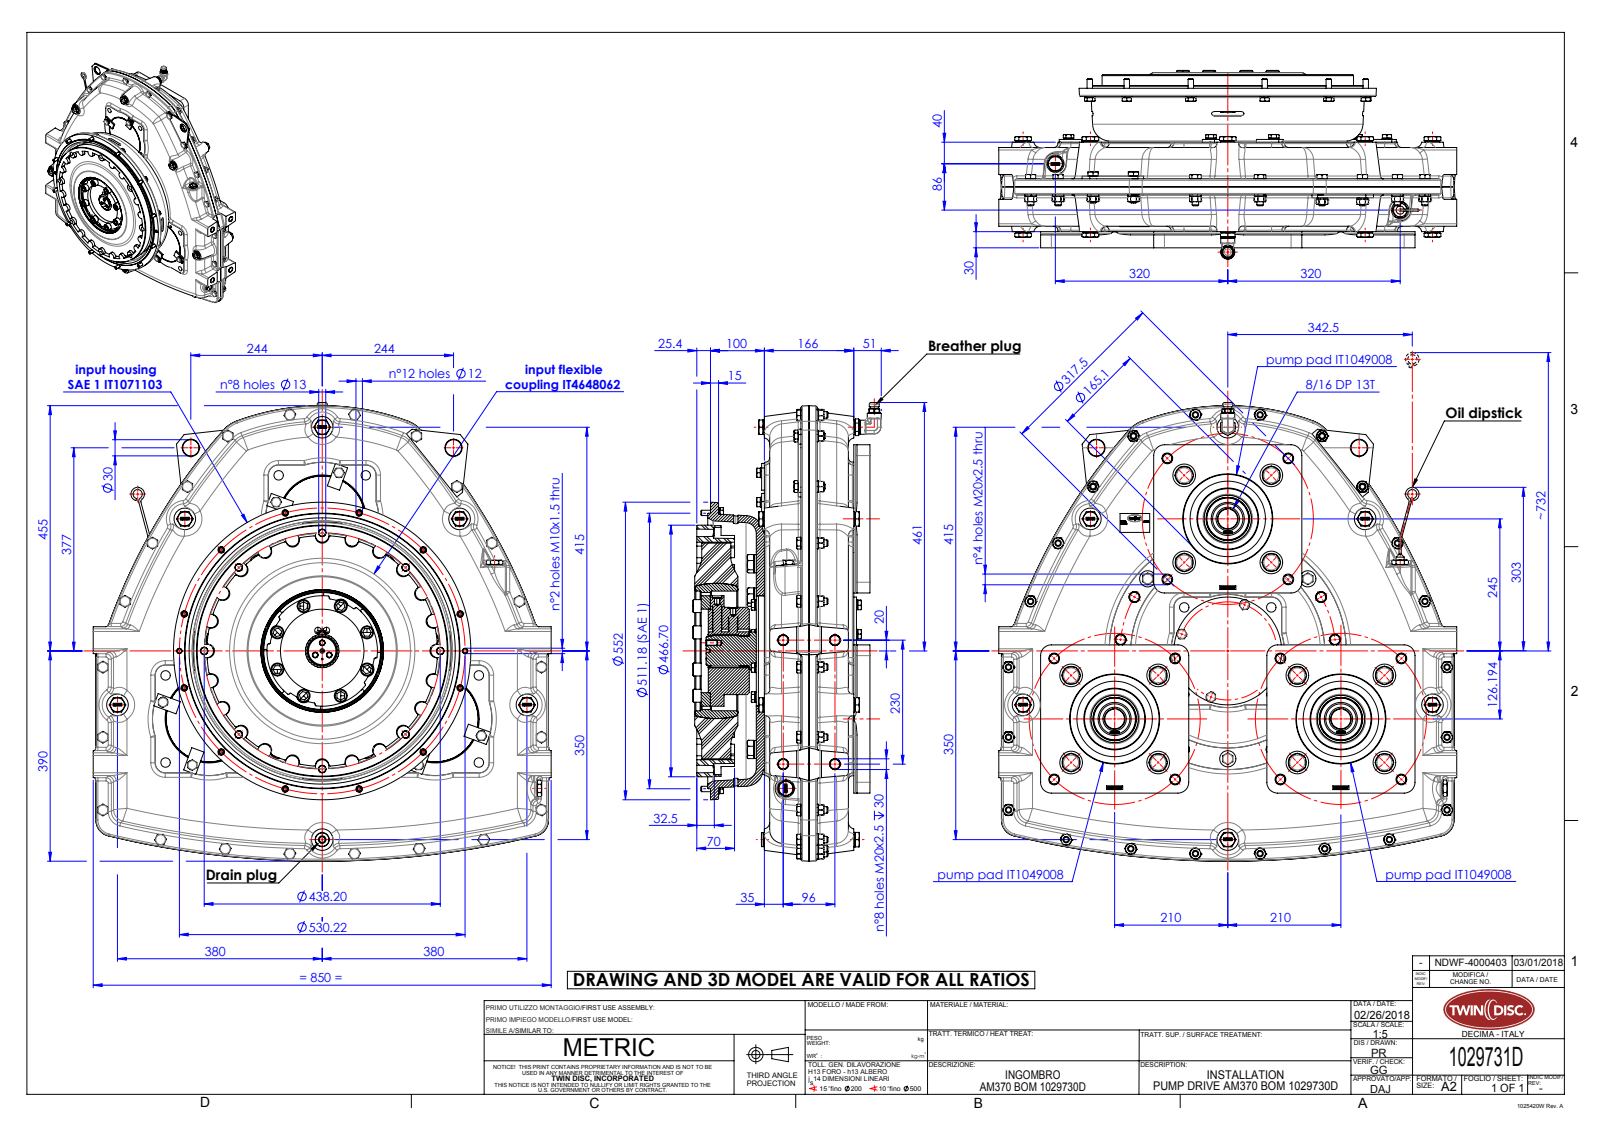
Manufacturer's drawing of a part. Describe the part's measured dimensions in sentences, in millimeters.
The part is named "ITam370-002_rev00-installation; IT2021490_rev00-installation; ITam270-014_rev00-installation; ITam365-006_rev00-installation (+8 more)". Its 3-D file was written by "SolidWorks 2015 (AUTOMOTIVE_DESIGN)". It is 76 solids with 11309 faces: 4586 planar, 3540 cylindrical and 3183 other. Overall it measures 850.8 by 850 by 350.2 millimeters. Its volume is 23 260 000 cubic millimeters and its surface area 7 400 000 square millimeters. Round holes: 42 of diameter 17.5, 37 of diameter 8.5, 36 of diameter 13, 25 of diameter 10.2, 25 of diameter 12.2, 21 of diameter 10.3, 20 of diameter 20.2, 19 of diameter 12, 18 of diameter 21, 14 of diameter 11, 14 of diameter 14, 12 of diameter 22. Round bosses or shafts: 32 of diameter 20, 28 of diameter 10, 25 of diameter 21.1, 25 of diameter 18.1, 25 of diameter 18, 25 of diameter 16.2, 21 of diameter 12, 20 of diameter 33.6. Partial cylindrical surfaces (rounded edges, fillets, slot ends): 274 of radius 0.35, 216 of radius 38.33, 72 of radius 12.5, 58 of radius 0.45, 58 of radius 29.02, 58 of radius 29.53, 46 of radius 2.5, 32 of radius 19. The main face-to-face distances are 83, 73, 10, 156, 98, 15, 30, 166, 146, 113. The hole center spacings are 814, 114.3, 161.64, 687.31, 45.28, 53.49, 75.29, 96.
